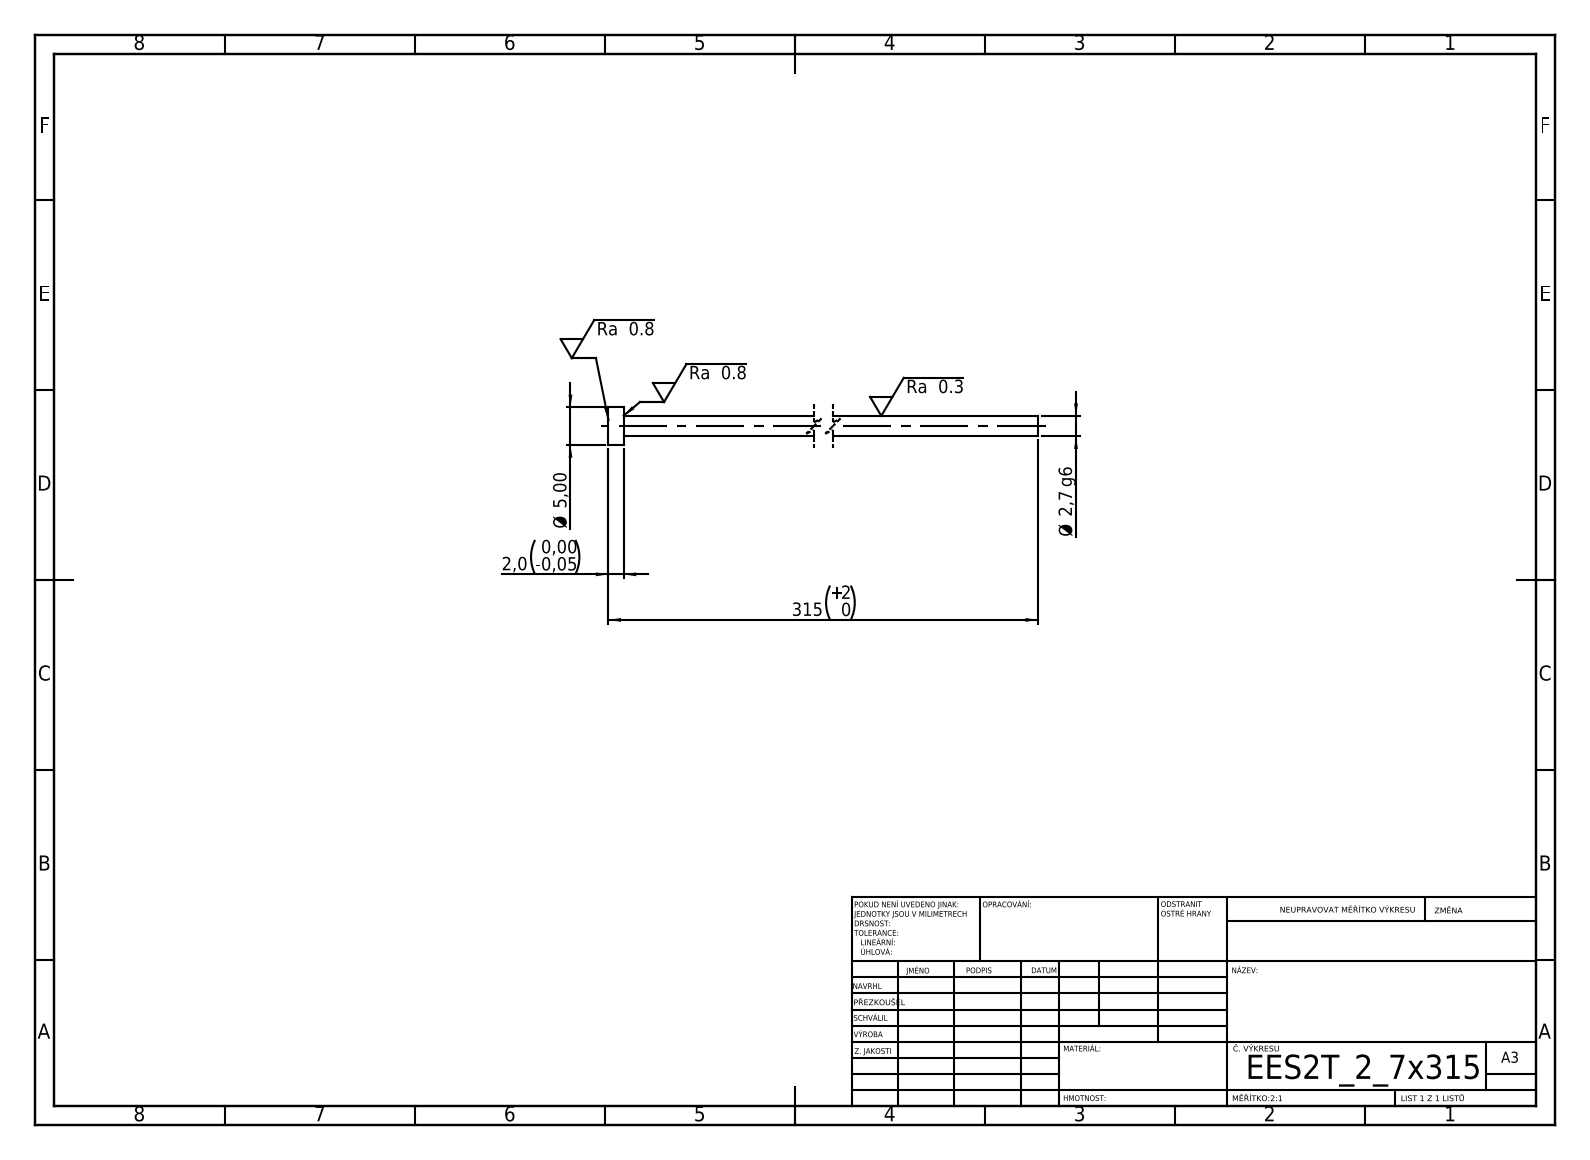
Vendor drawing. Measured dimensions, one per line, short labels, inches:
written by: SolidWorks 2019 (CONFIG_CONTROL_DESIGN)
unit: in
bodies: 1 solid, 7 faces (3 planar, 4 cylindrical, 0 other)
size: 12.402 × 0.197 × 0.197
volume: 0.112 in³; area: 4.225 in²
bosses: 1× ⌀0.197, 1× ⌀0.106
face distances: 0.079, 12.402, 12.323
